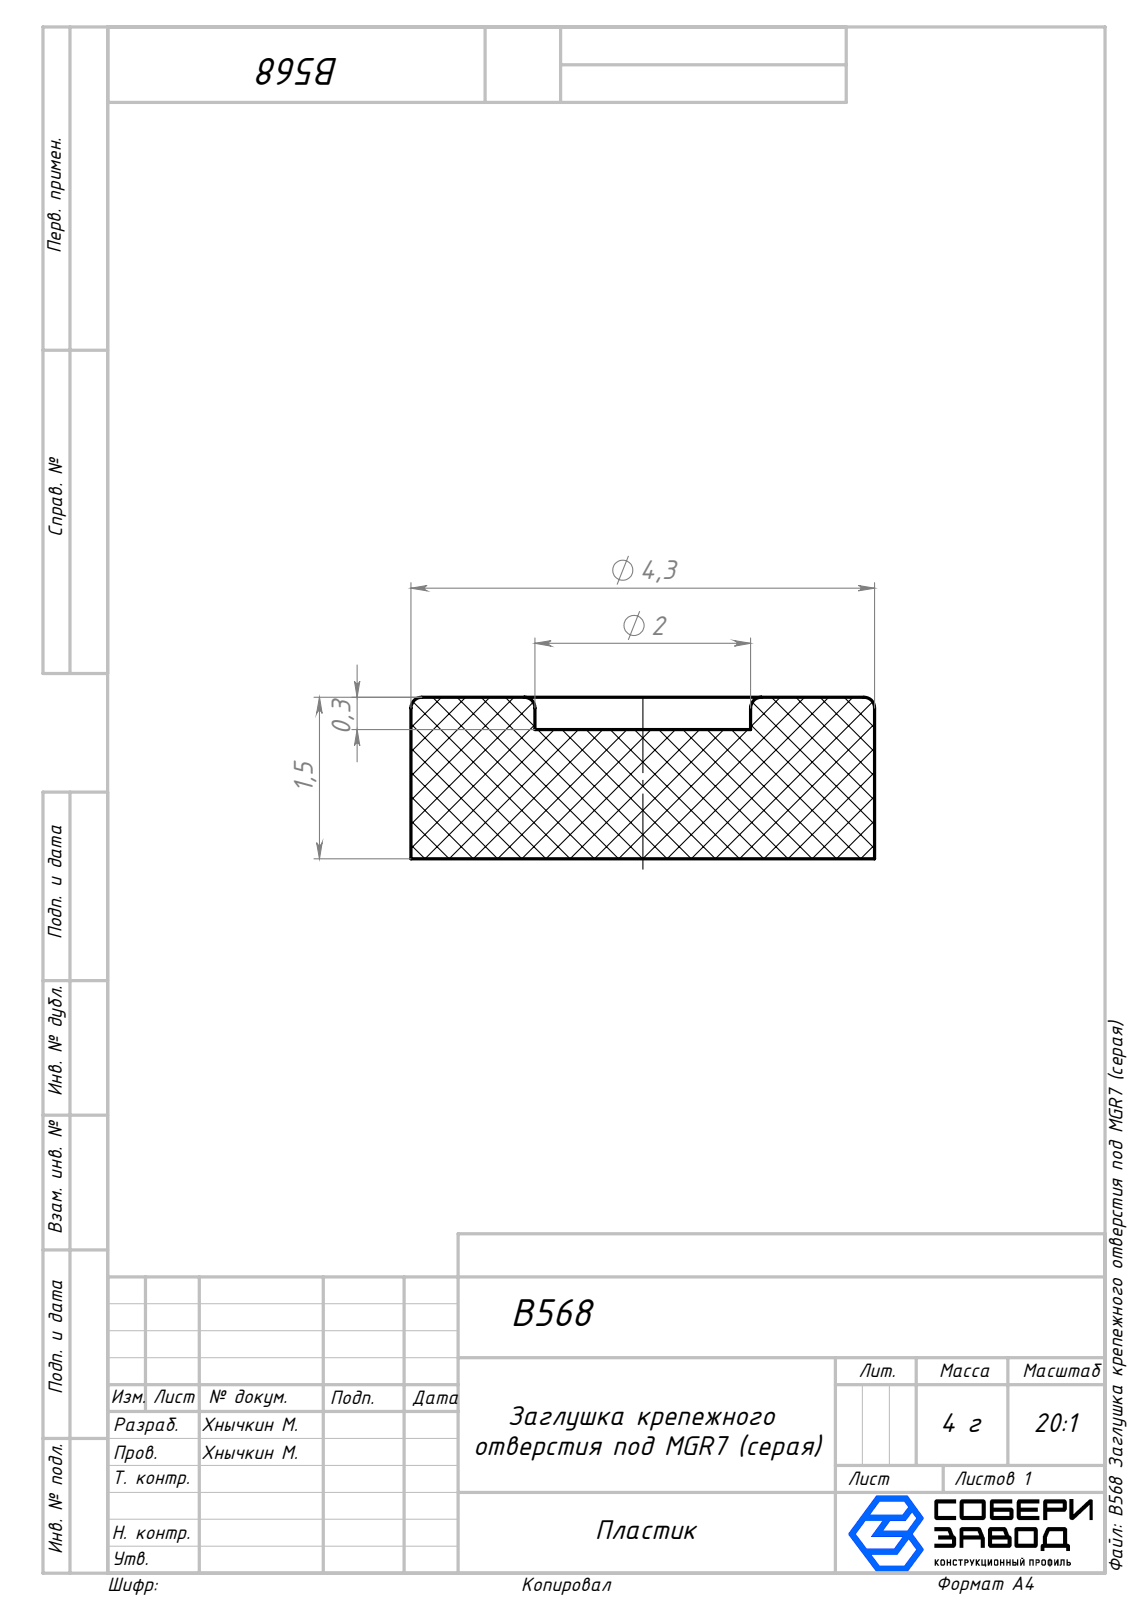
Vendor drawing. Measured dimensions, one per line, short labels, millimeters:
name: B568 Заглушка крепежного отверстия под MGR7 (серая)
written by: SolidWorks 2026 (AUTOMOTIVE_DESIGN)
unit: mm
bodies: 1 solid, 11 faces (3 planar, 4 cylindrical, 4 other)
size: 4.3 × 4.3 × 1.5
volume: 21 mm³; area: 50 mm²
holes: 1× ⌀2
bosses: 1× ⌀4.3
face distances: 1.5, 1.2
